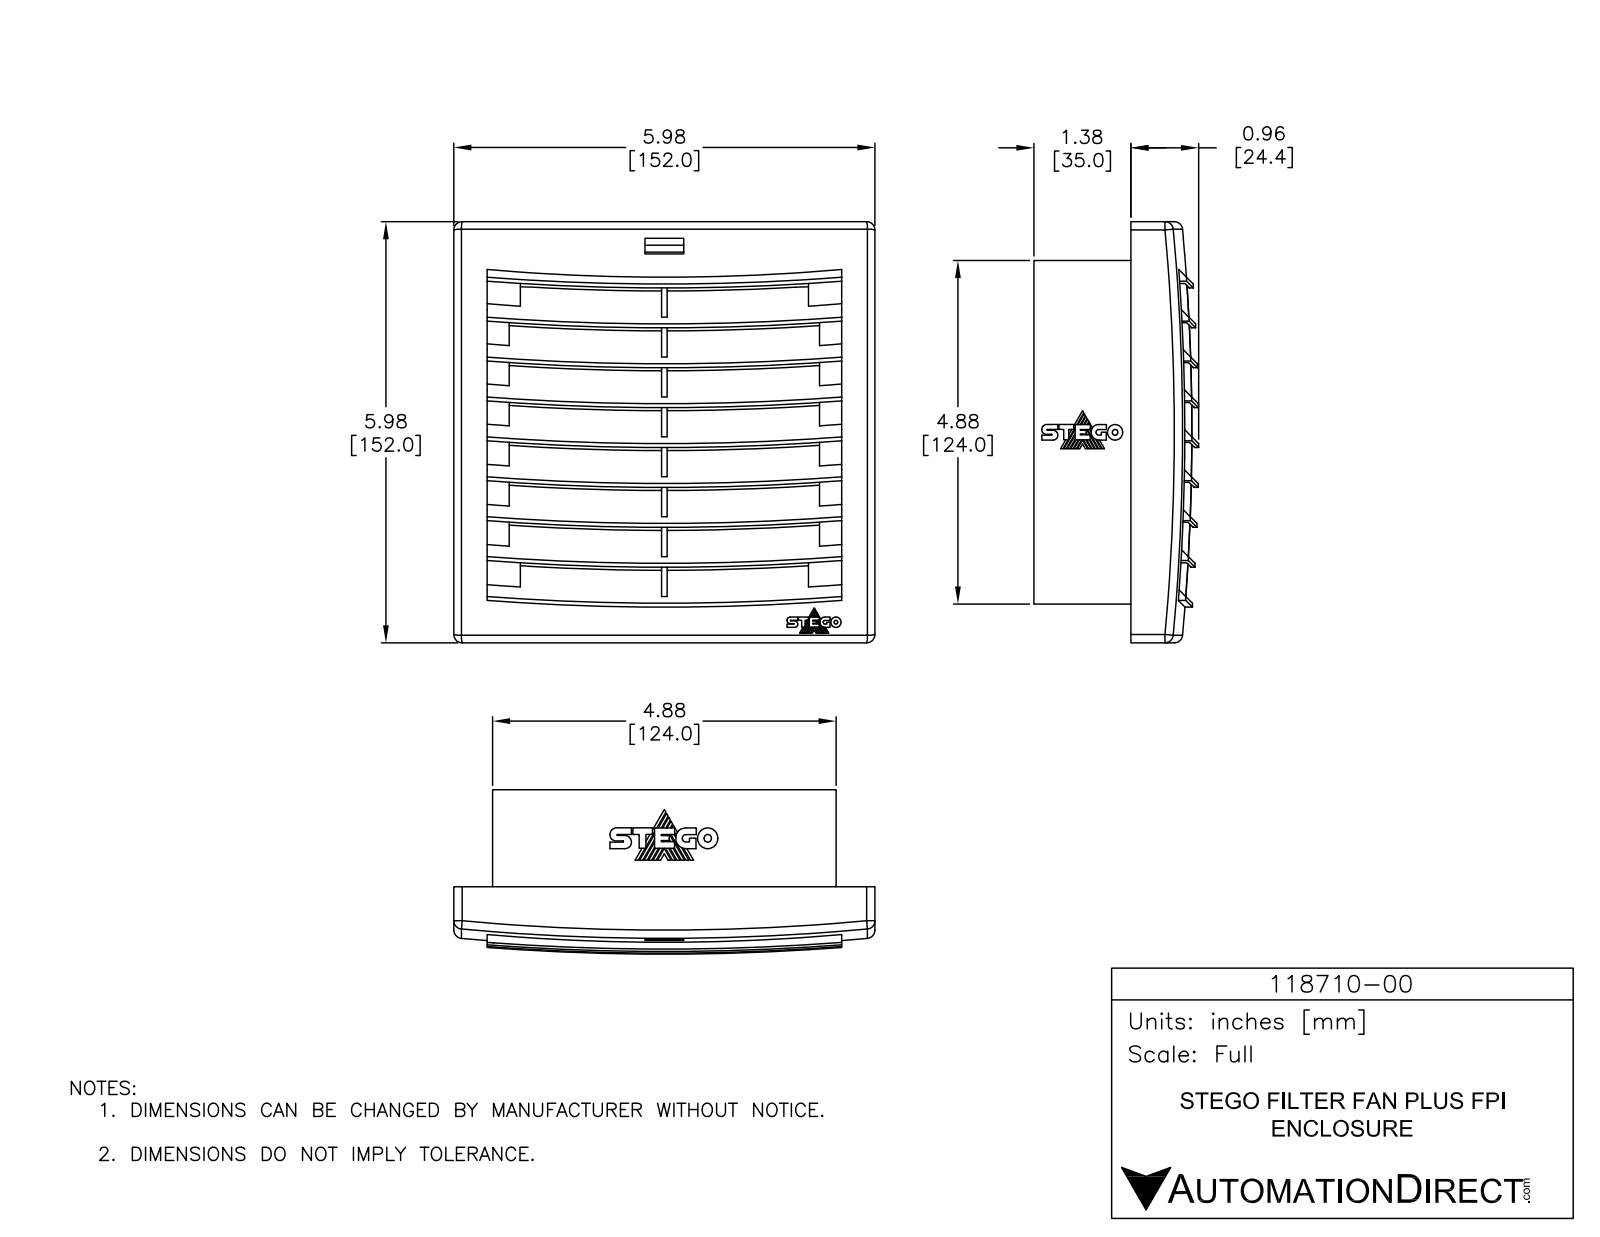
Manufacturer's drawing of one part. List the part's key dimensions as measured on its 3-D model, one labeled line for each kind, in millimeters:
Part name (STEP PRODUCT): 118710-00
STEP written by: SolidWorks 2018 (AUTOMOTIVE_DESIGN)
Units: millimetres
Bodies: 1 solid, 341 faces (193 planar, 148 cylindrical, 0 other)
Overall size (bounding box): 152 × 152 × 60
Volume: 318 900 mm³ · Surface area: 167 200 mm²
Round holes (diameter × count): ⌀65.5 ×1, ⌀83.9 ×1, ⌀105.4 ×1
Round bosses / shafts (diameter × count): ⌀89.9 ×1, ⌀71.5 ×1
Partial cylindrical surfaces — rounded edges, fillets, slot ends (radius × count): R349.4 ×16, R3 ×4, R15.8 ×1, R23.5 ×1, R26.5 ×1, R293.8 ×1
Main face-to-face distances: 1.5, 10.8, 3.1, 120.9, 21.6, 3.4, 6.8, 12.3, 9.3, 117.8
